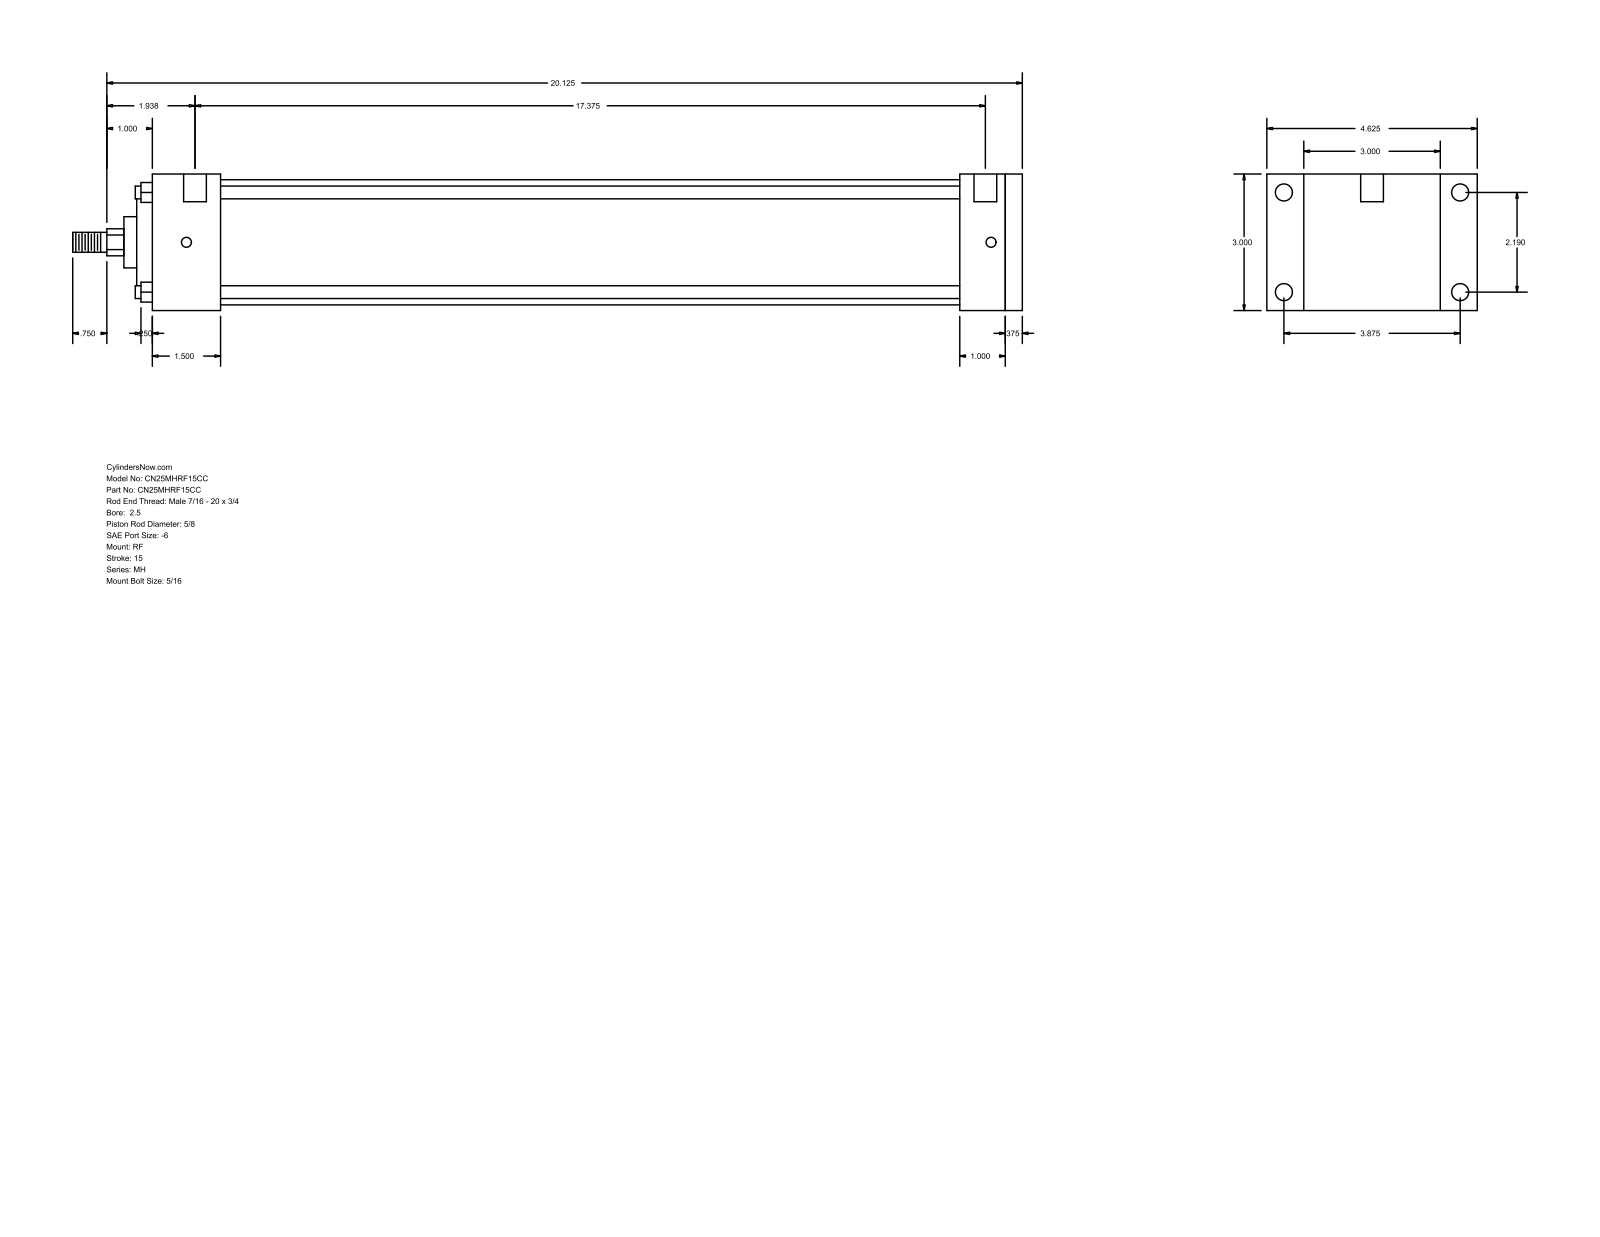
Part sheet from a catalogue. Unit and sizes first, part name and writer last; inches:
Units: inches
Overall size (bounding box): 20.875 × 4.625 × 3
Round holes (diameter × count): ⌀0.219 ×4, ⌀0.375 ×4, ⌀0.5 ×2
Round bosses / shafts (diameter × count): ⌀0.281 ×4, ⌀2.75 ×1, ⌀2.187 ×1, ⌀1.125 ×1, ⌀0.625 ×1, ⌀0.437 ×1
Partial cylindrical surfaces — rounded edges, fillets, slot ends (radius × count): R0.297 ×1
Main face-to-face distances: 3, 0.375, 19.125, 18.75, 1, 1.375, 1.5, 17.75, 16.25, 17.25
Hole centre spacings: 2.19, 3.875, 4.451, 17.687, 0.125, 0.187, 17.375, 17.5
Bodies: 0 solids, 94 faces (65 planar, 29 cylindrical, 0 other)
Part name (STEP PRODUCT): MH_RF__0250_0.625
STEP written by: GSSL Pune (CONFIG_CONTROL_DESIGN)
